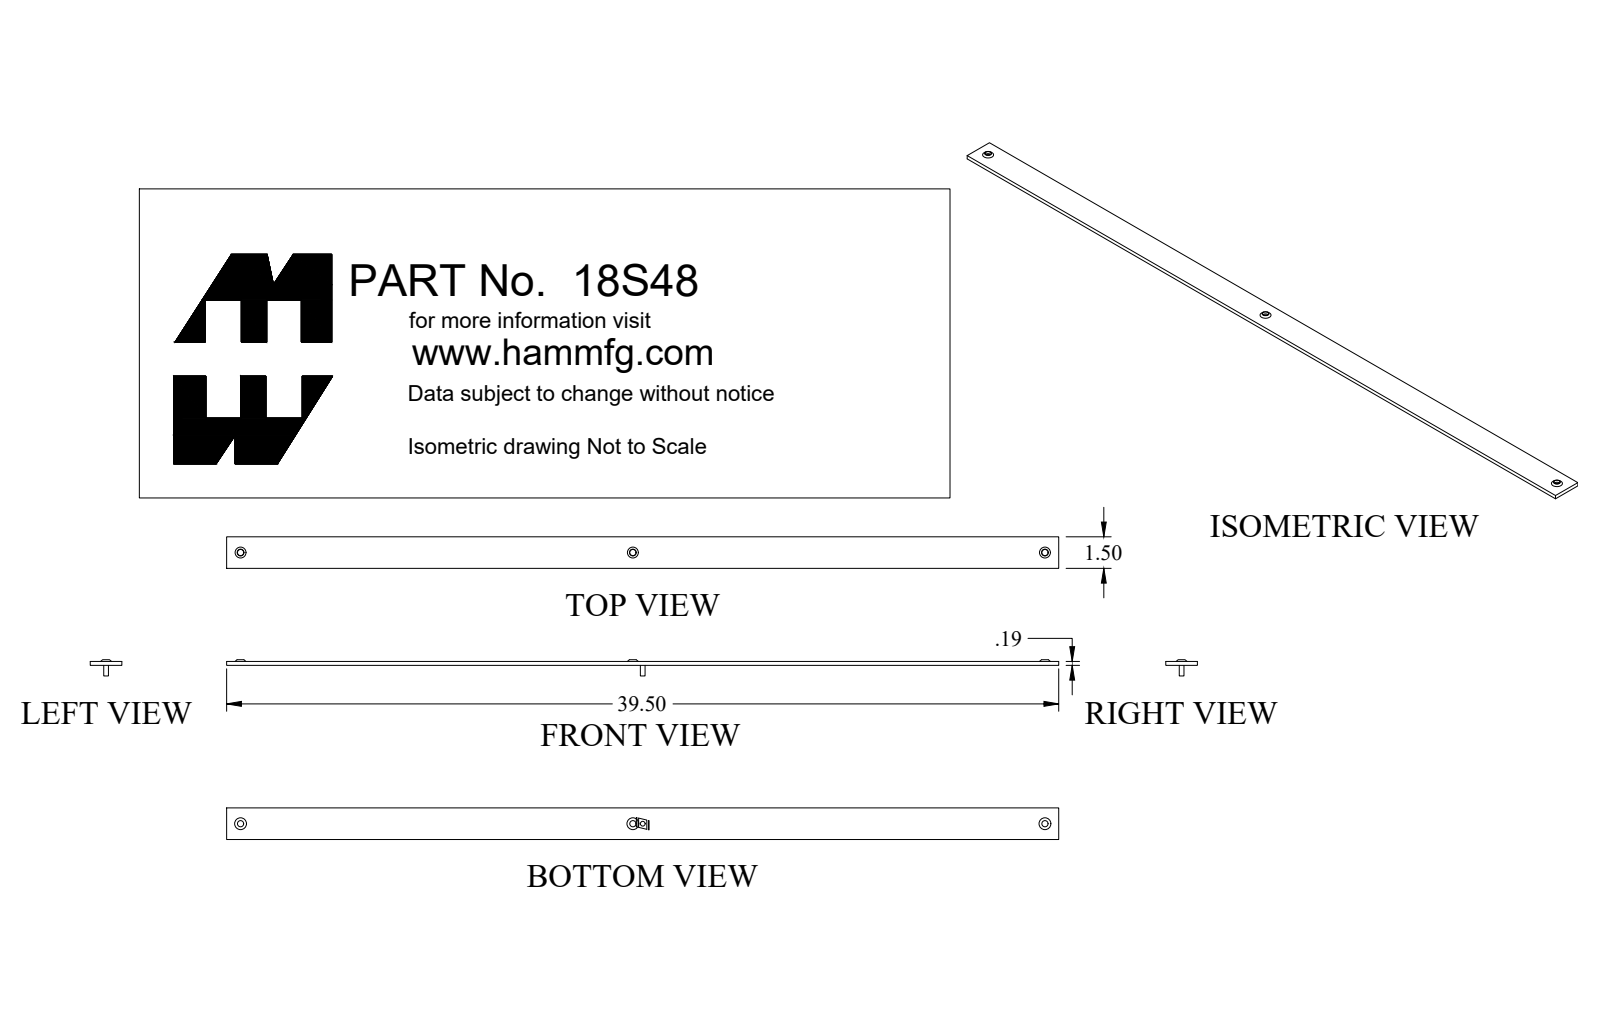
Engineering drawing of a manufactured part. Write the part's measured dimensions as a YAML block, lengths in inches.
part_name: "18S48_Default"
step_written_by: "SolidWorks 2018 (CONFIG_CONTROL_DESIGN)"
units: inches
bodies: {solids: 1, faces: 27, planar: 9, cylindrical: 6, other: 12}
overall_size: [39.5, 1.5, 0.27]
volume: 11.08
surface_area: 134.2
round_holes:
  - {diameter: 0.296, count: 3}
face_to_face_distances: [0.188, 1.5, 39.5, 0.27, 0.082]
hole_center_spacings: [18.625, 19.563, 38.188]
